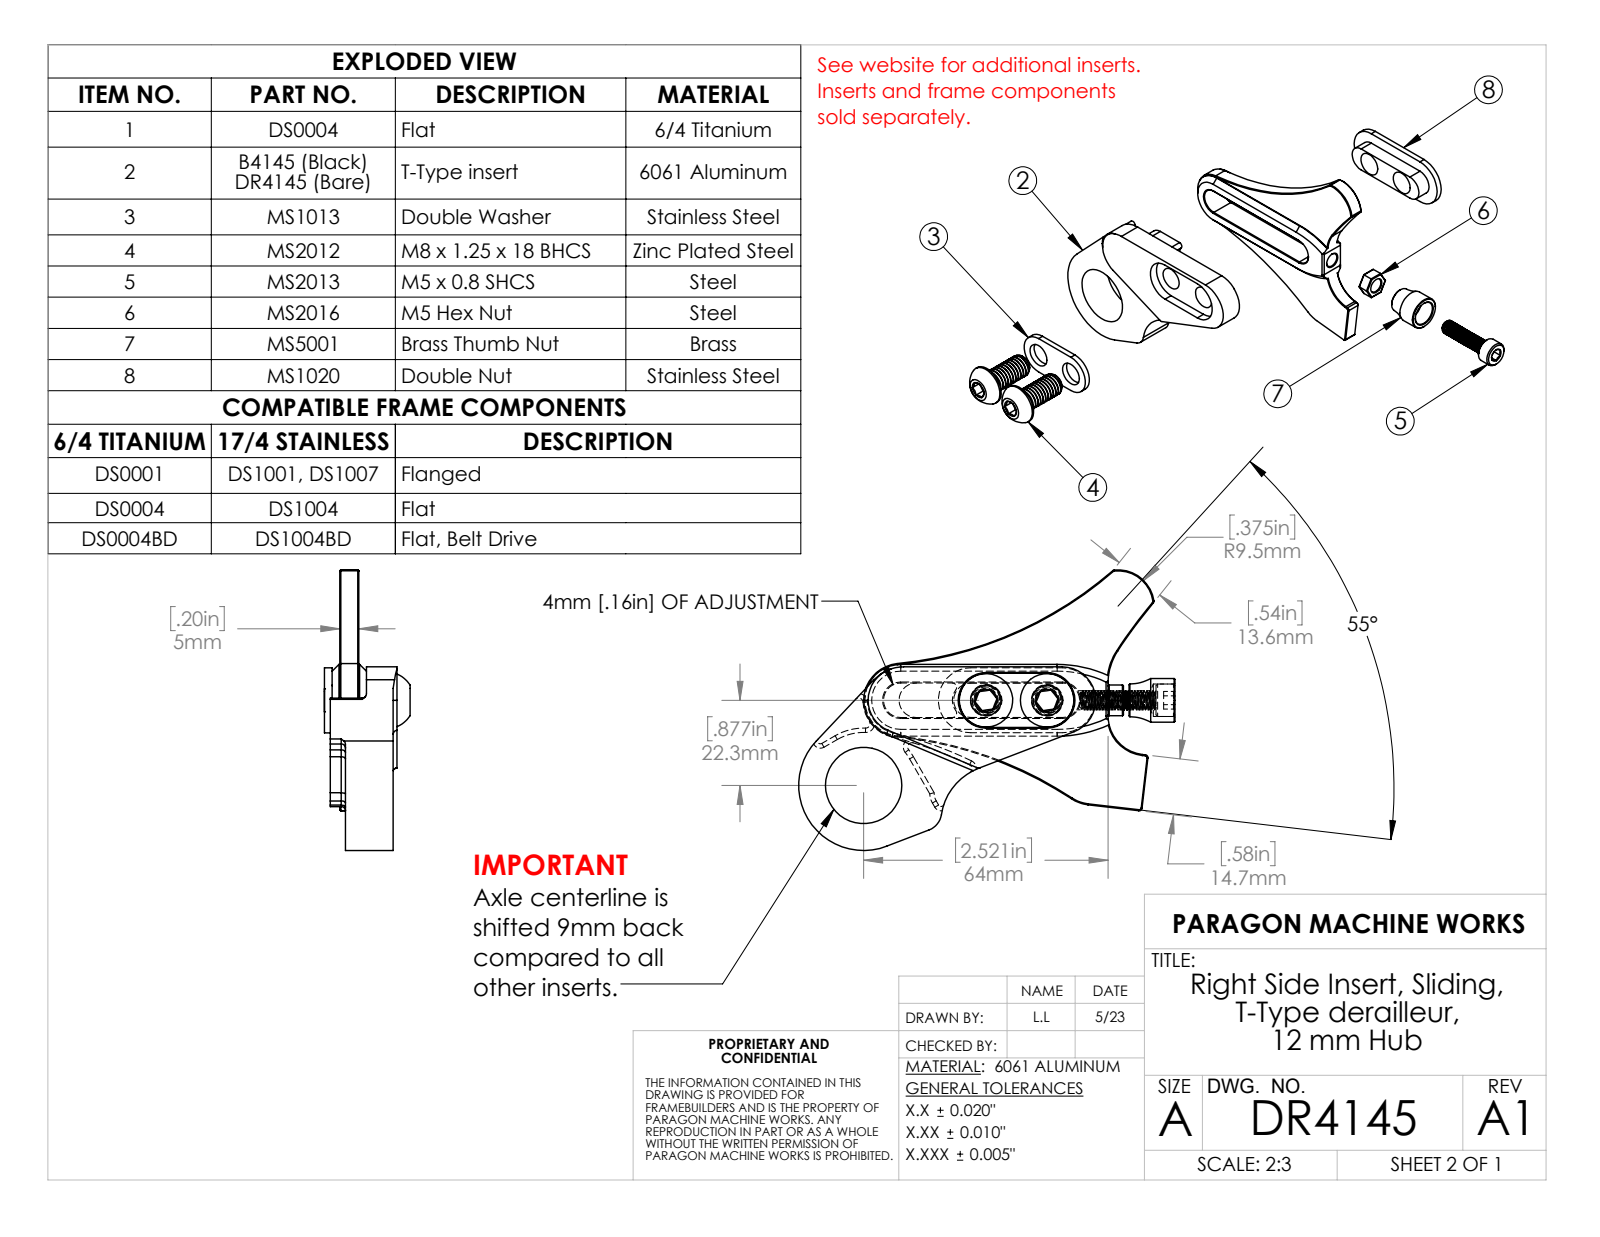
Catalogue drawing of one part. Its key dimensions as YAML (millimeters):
part_name: "DS0004; MS5001; MS1020; 2-HOLE_WASHER (+5 more)"
step_written_by: "SolidWorks 2022 (AUTOMOTIVE_DESIGN)"
units: millimeters
bodies: {solids: 9, faces: 504, planar: 104, cylindrical: 267, other: 133}
overall_size: [200.2, 162.1, 73.5]
volume: 38070
surface_area: 21610
round_holes:
  - {diameter: 7.9, count: 2}
  - {diameter: 8.3, count: 2}
  - {diameter: 8.5, count: 1}
  - {diameter: 20, count: 1}
round_bosses_or_shafts:
  - {diameter: 14, count: 2}
  - {diameter: 8, count: 2}
  - {diameter: 11.4, count: 1}
  - {diameter: 5, count: 1}
  - {diameter: 4, count: 1}
partial_cylinders:
  - {radius: 0.3, count: 12}
  - {radius: 1.1, count: 11}
  - {radius: 0.8, count: 6}
  - {radius: 4.5, count: 4}
  - {radius: 4.5, count: 2}
  - {radius: 7.1, count: 2}
  - {radius: 7.3, count: 2}
  - {radius: 8.5, count: 2}
face_to_face_distances: [5, 2, 8, 45.1, 7, 52.8, 59.8, 53.1, 48.1, 40.1]
hole_center_spacings: [16, 39, 53]
